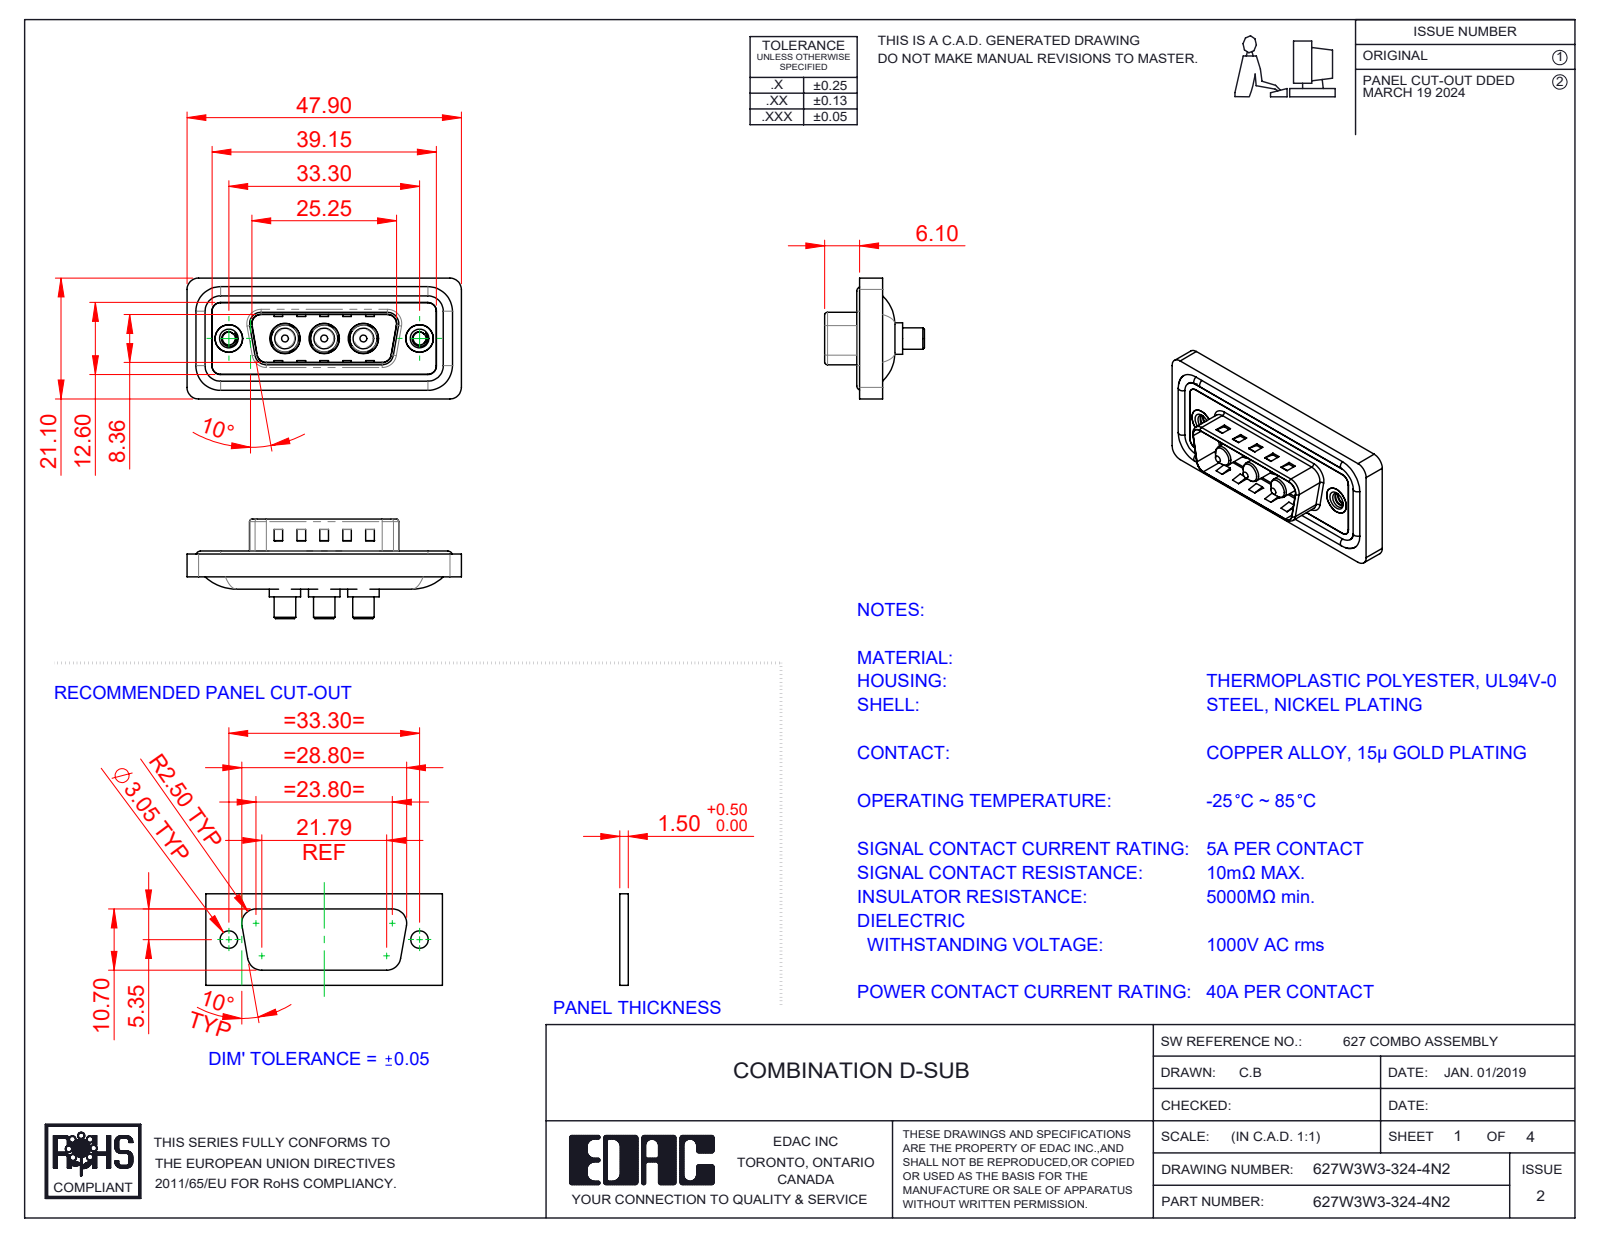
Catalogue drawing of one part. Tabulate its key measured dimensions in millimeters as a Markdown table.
| quantity | value |
| --- | --- |
| part name | 627Combo Shell Front_15 Contacts; 627Combo Shell Rear_15 Contacts; 627W3W3-324-4N2; 627Combo Threaded Rivet_2 (+3 more) |
| STEP written by | SolidWorks 2023 (CONFIG_CONTROL_DESIGN) |
| units | millimeters |
| bodies | 13 solids, 564 faces (207 planar, 241 cylindrical, 116 other) |
| overall size | 47.9 × 21.1 × 17.4 |
| volume | 5 641 mm³ |
| surface area | 8 786 mm² |
| round holes (diameter × count) | 4.85 × 3, 5.3 × 3, 2.26 × 2, 4 × 2, 4.8 × 2, 5 × 2 |
| round bosses / shafts (diameter × count) | 1.6 × 4, 5.5 × 3, 5.2 × 3, 4.75 × 3, 3.75 × 3, 3.6 × 3, 4.9 × 2 |
| partial cylindrical surfaces (radius × count) | 1.5 × 26, 2 × 20, 0.5 × 8, 1.6 × 8, 0.25 × 4, 0.6 × 4, 0.65 × 4, 0.9 × 4 |
| main face-to-face distances | 0.4, 1.1, 1.5, 0.5, 1.6, 3.1, 2.9, 4, 0.82, 9.58 |
| hole center spacings | 6.85, 9.8, 16.65, 23.5, 13.7, 33.3 |
